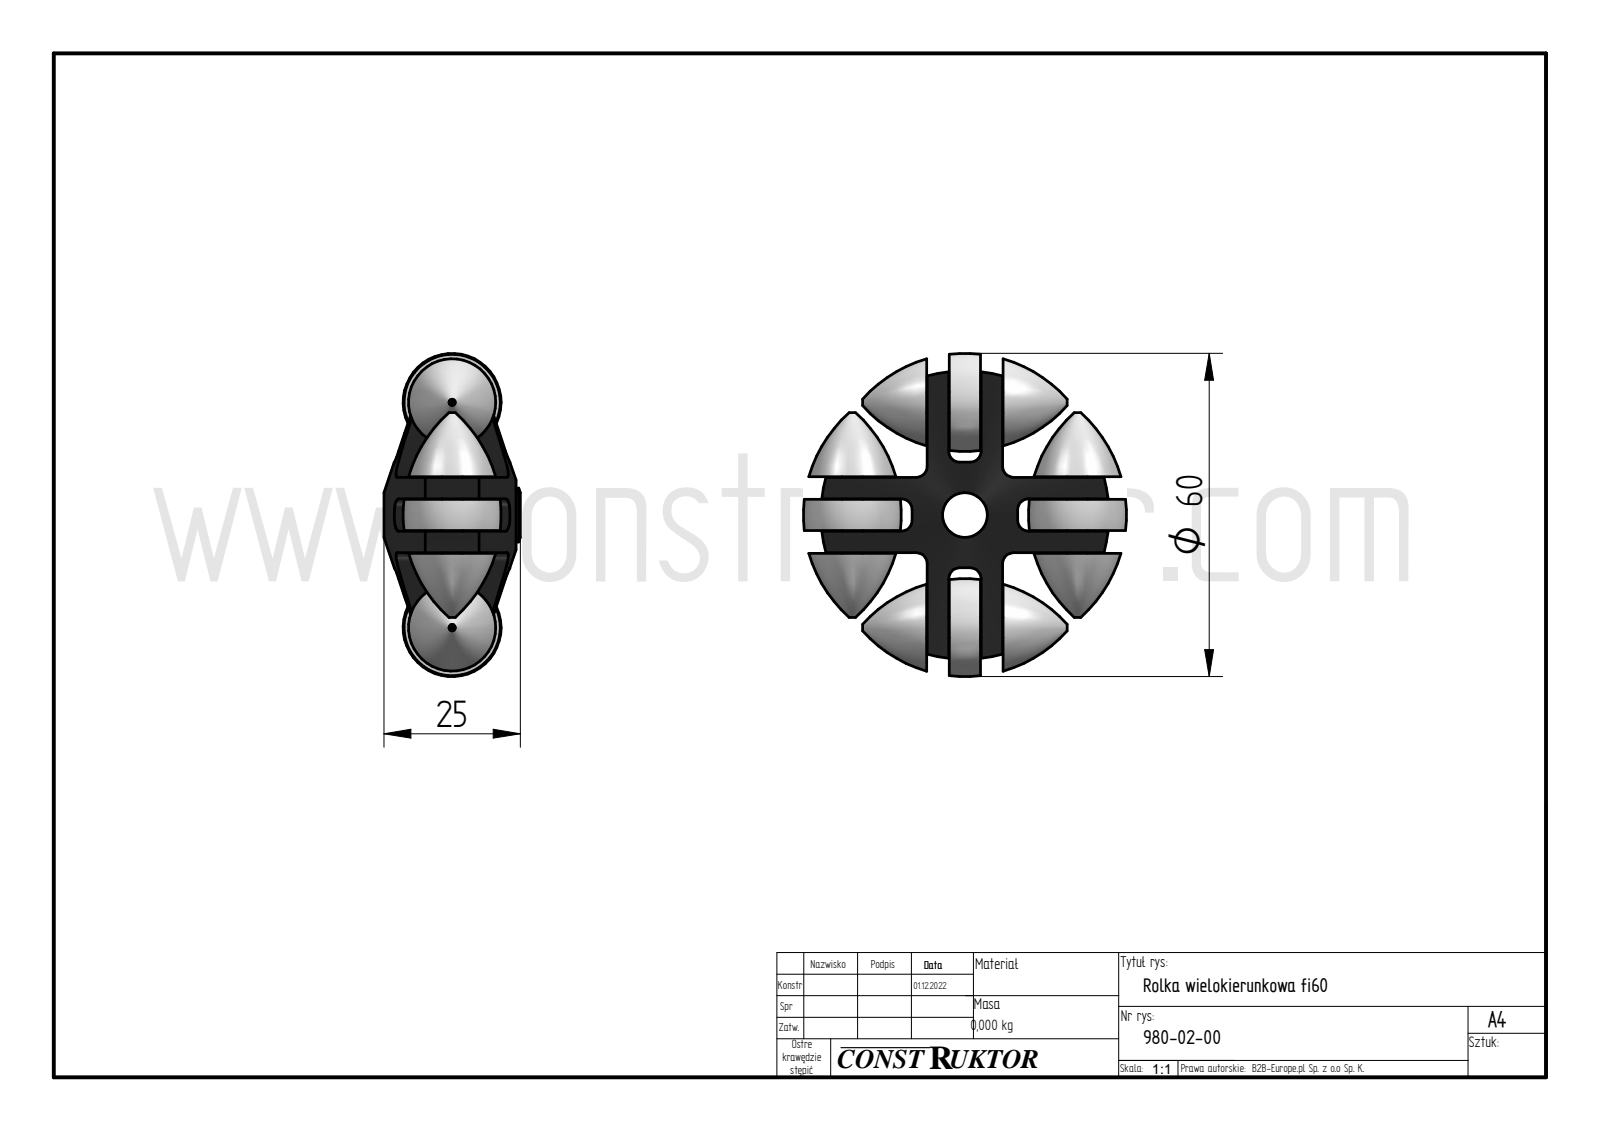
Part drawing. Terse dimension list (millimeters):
name: 980-02-00; 980-02-01; 980-02-02
written by: ST-DEVELOPER v16.7 (AUTOMOTIVE_DESIGN)
unit: mm
bodies: 5 solids, 118 faces (60 planar, 43 cylindrical, 15 other)
size: 59.98 × 59.98 × 25.3
volume: 29 996 mm³; area: 16 916 mm²
holes: 4× ⌀0.2, 4× ⌀4, 1× ⌀8.3, 1× ⌀13
bosses: 4× ⌀3.8, 1× ⌀10
rounds: 12× R2, 1× R26.75
face distances: 4.1, 10, 9.9, 4, 5.9, 4.2, 10.1, 14.1, 14, 5.8
hole spacings: 41.8
